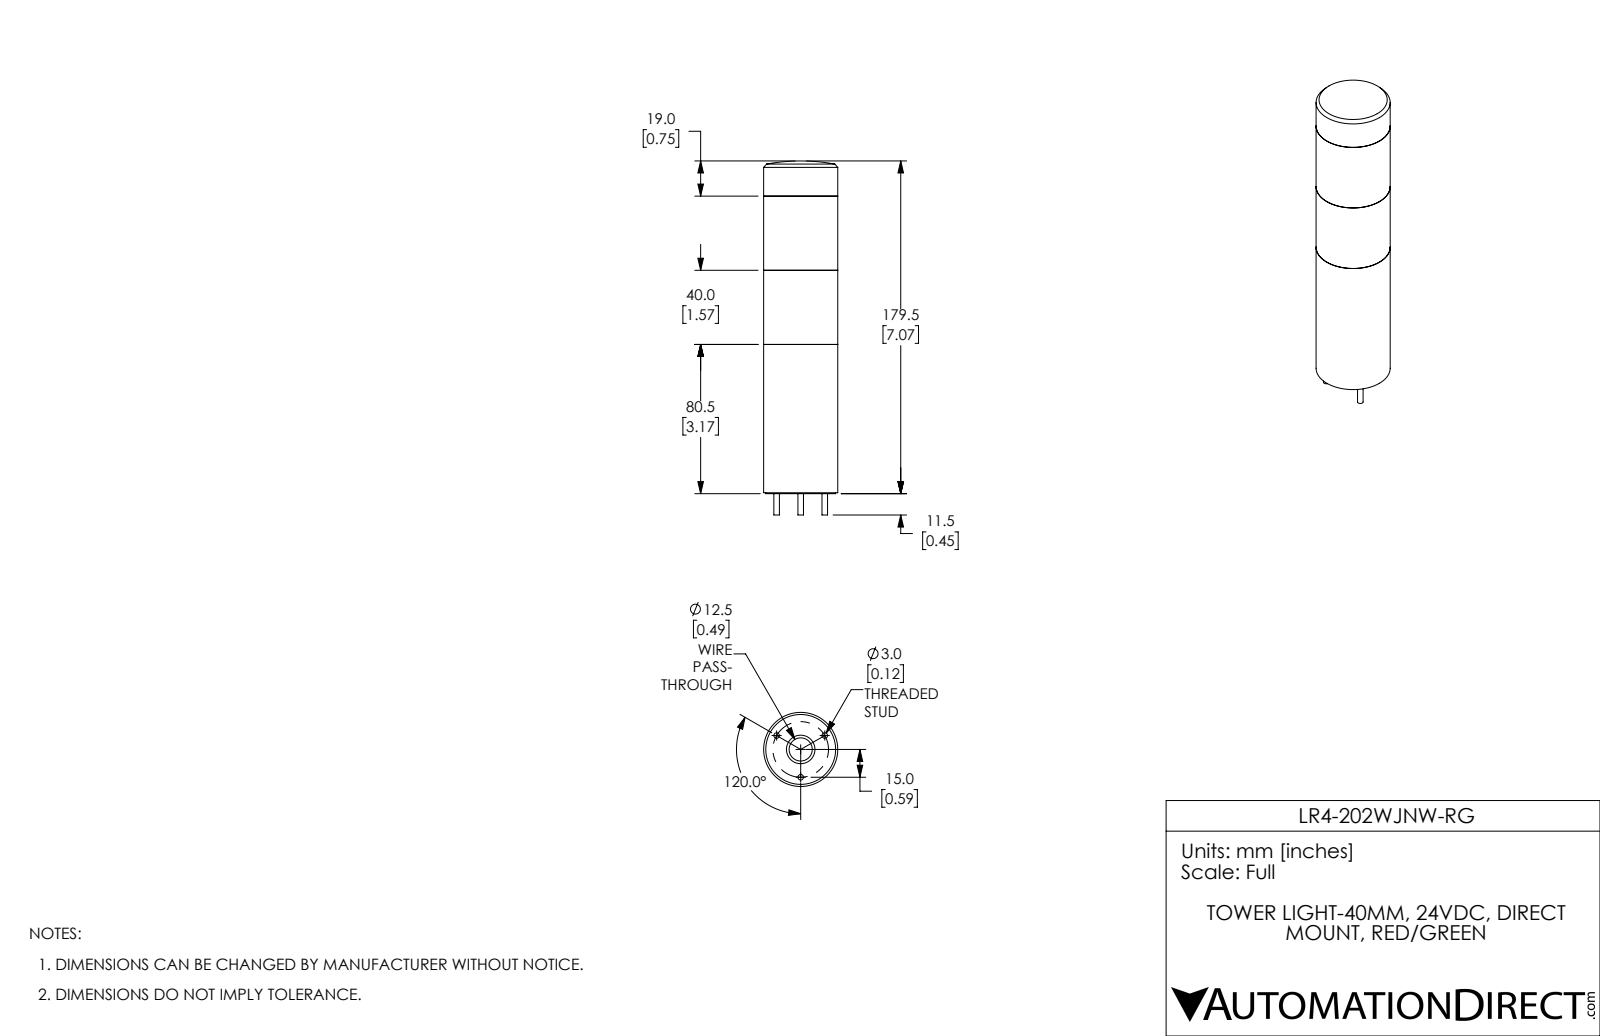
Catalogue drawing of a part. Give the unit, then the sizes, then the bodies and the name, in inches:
Units: inches
Overall size (bounding box): 7.519 × 1.575 × 1.575
Round holes (diameter × count): ⌀0.492 ×1, ⌀0.606 ×1, ⌀1.366 ×1, ⌀1.386 ×1, ⌀1.461 ×1, ⌀1.463 ×1
Round bosses / shafts (diameter × count): ⌀0.118 ×3, ⌀1.575 ×1, ⌀1.484 ×1
Main face-to-face distances: 1.575, 3.15, 0.406, 3.575, 5.15, 6.724, 0.126, 0.28, 1.98, 1.169
Volume: 13.65 in³ · Surface area: 61.58 in²
Bodies: 4 solids, 72 faces (25 planar, 44 cylindrical, 3 other)
Part name (STEP PRODUCT): LR4-202WJNW-RG
STEP written by: SolidWorks 2017 (AUTOMOTIVE_DESIGN)
